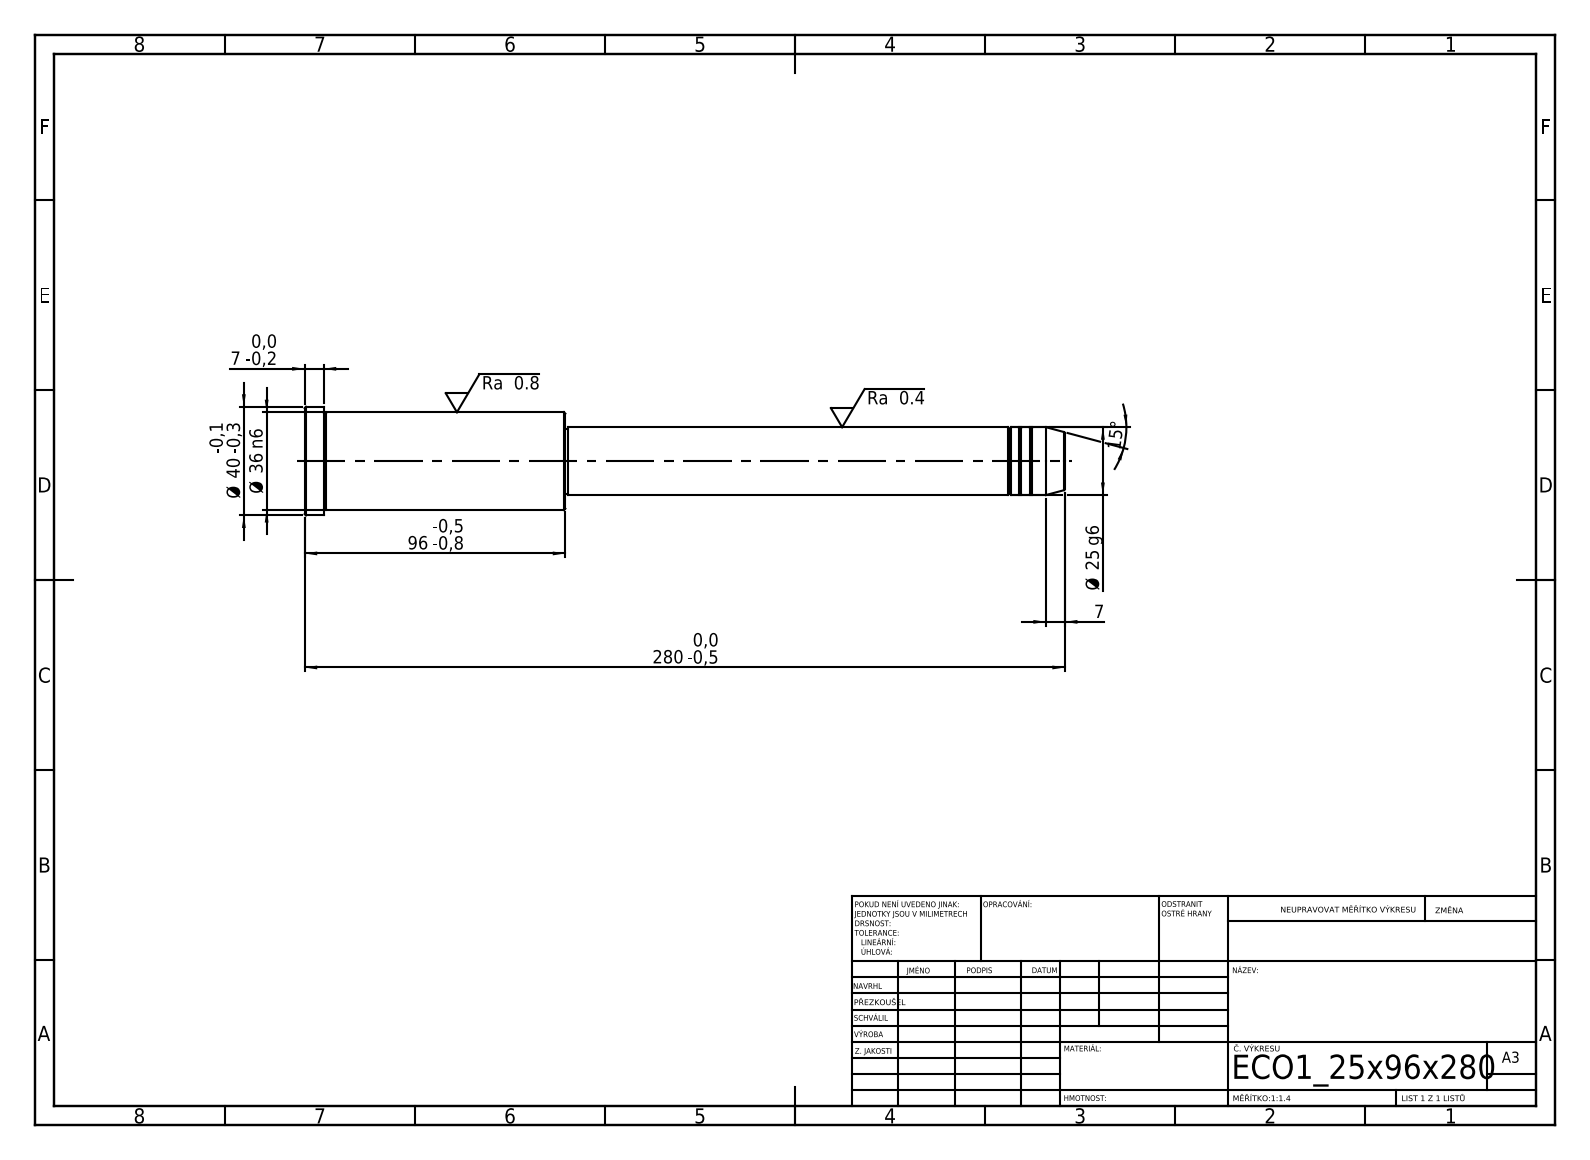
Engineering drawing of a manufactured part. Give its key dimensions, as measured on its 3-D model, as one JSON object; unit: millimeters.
{"step_written_by": "SolidWorks 2019 (CONFIG_CONTROL_DESIGN)", "units": "millimeters", "bodies": {"solids": 1, "faces": 43, "planar": 5, "cylindrical": 14, "other": 24}, "overall_size": [280, 40, 40], "volume_mm3": 189014, "surface_area_mm2": 27932, "round_bosses_or_shafts": [[40, 1], [36, 1], [25, 1], [24, 1]], "face_to_face_distances": [96, 184, 280, 273, 89, 7, 183, 1, 90, 97]}
